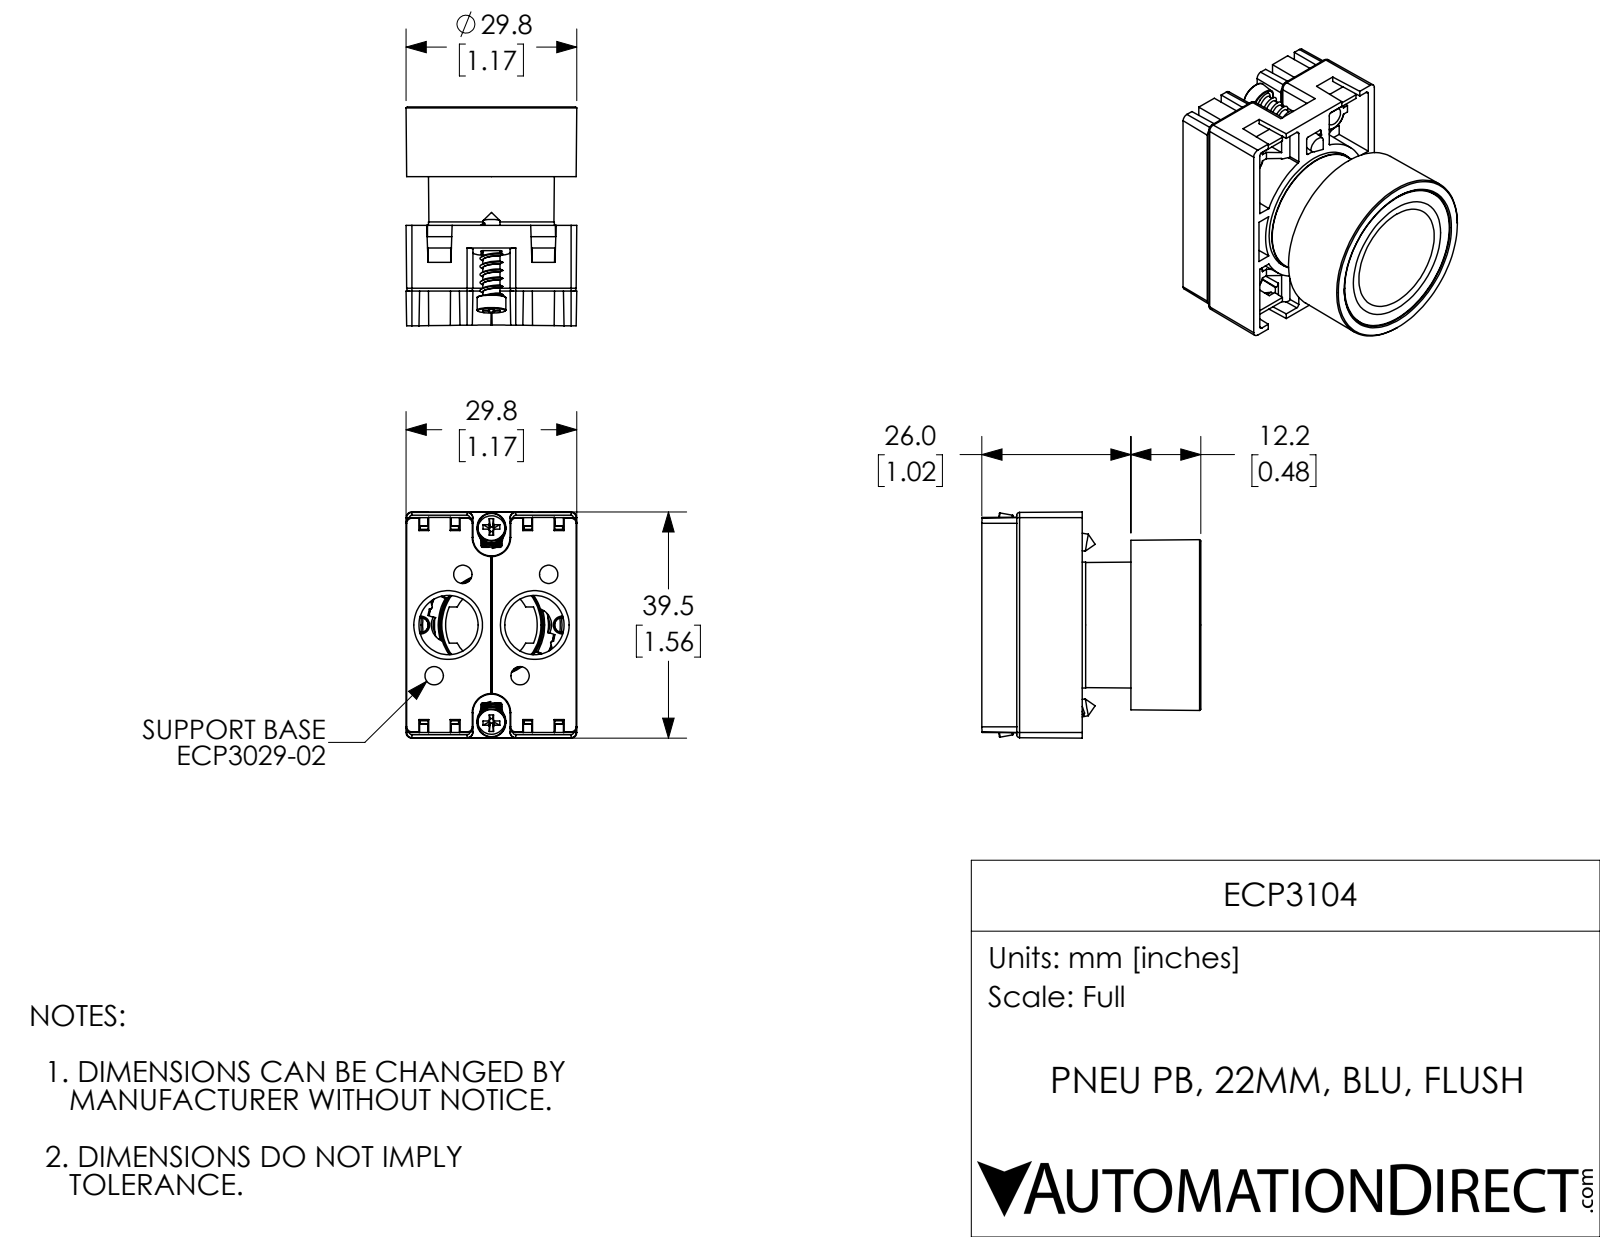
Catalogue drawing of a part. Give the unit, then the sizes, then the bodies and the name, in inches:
Units: inches
Overall size (bounding box): 1.555 × 1.505 × 1.173
Round holes (diameter × count): ⌀0.081 ×4, ⌀0.407 ×2, ⌀0.697 ×1, ⌀0.732 ×1
Round bosses / shafts (diameter × count): ⌀0.197 ×2, ⌀0.118 ×2, ⌀1.016 ×1, ⌀0.866 ×1
Partial cylindrical surfaces — rounded edges, fillets, slot ends (radius × count): R0.02 ×18, R0.006 ×8, R0.012 ×8, R0.008 ×4, R0.039 ×4, R0.008 ×2, R0.118 ×2, R0.128 ×2
Main face-to-face distances: 1.195, 0.963, 0.177, 0.067, 0.715, 0.744, 0.451, 0.587, 0.519, 0.256
Hole centre spacings: 0.304, 0.541, 0.817, 0.295, 0.472, 0.972, 1.081, 0.591
Volume: 0.893 in³ · Surface area: 29.03 in²
Bodies: 7 solids, 778 faces (363 planar, 131 cylindrical, 284 other)
Part name (STEP PRODUCT): ECP3104
STEP written by: SolidWorks 2017 (AUTOMOTIVE_DESIGN)
